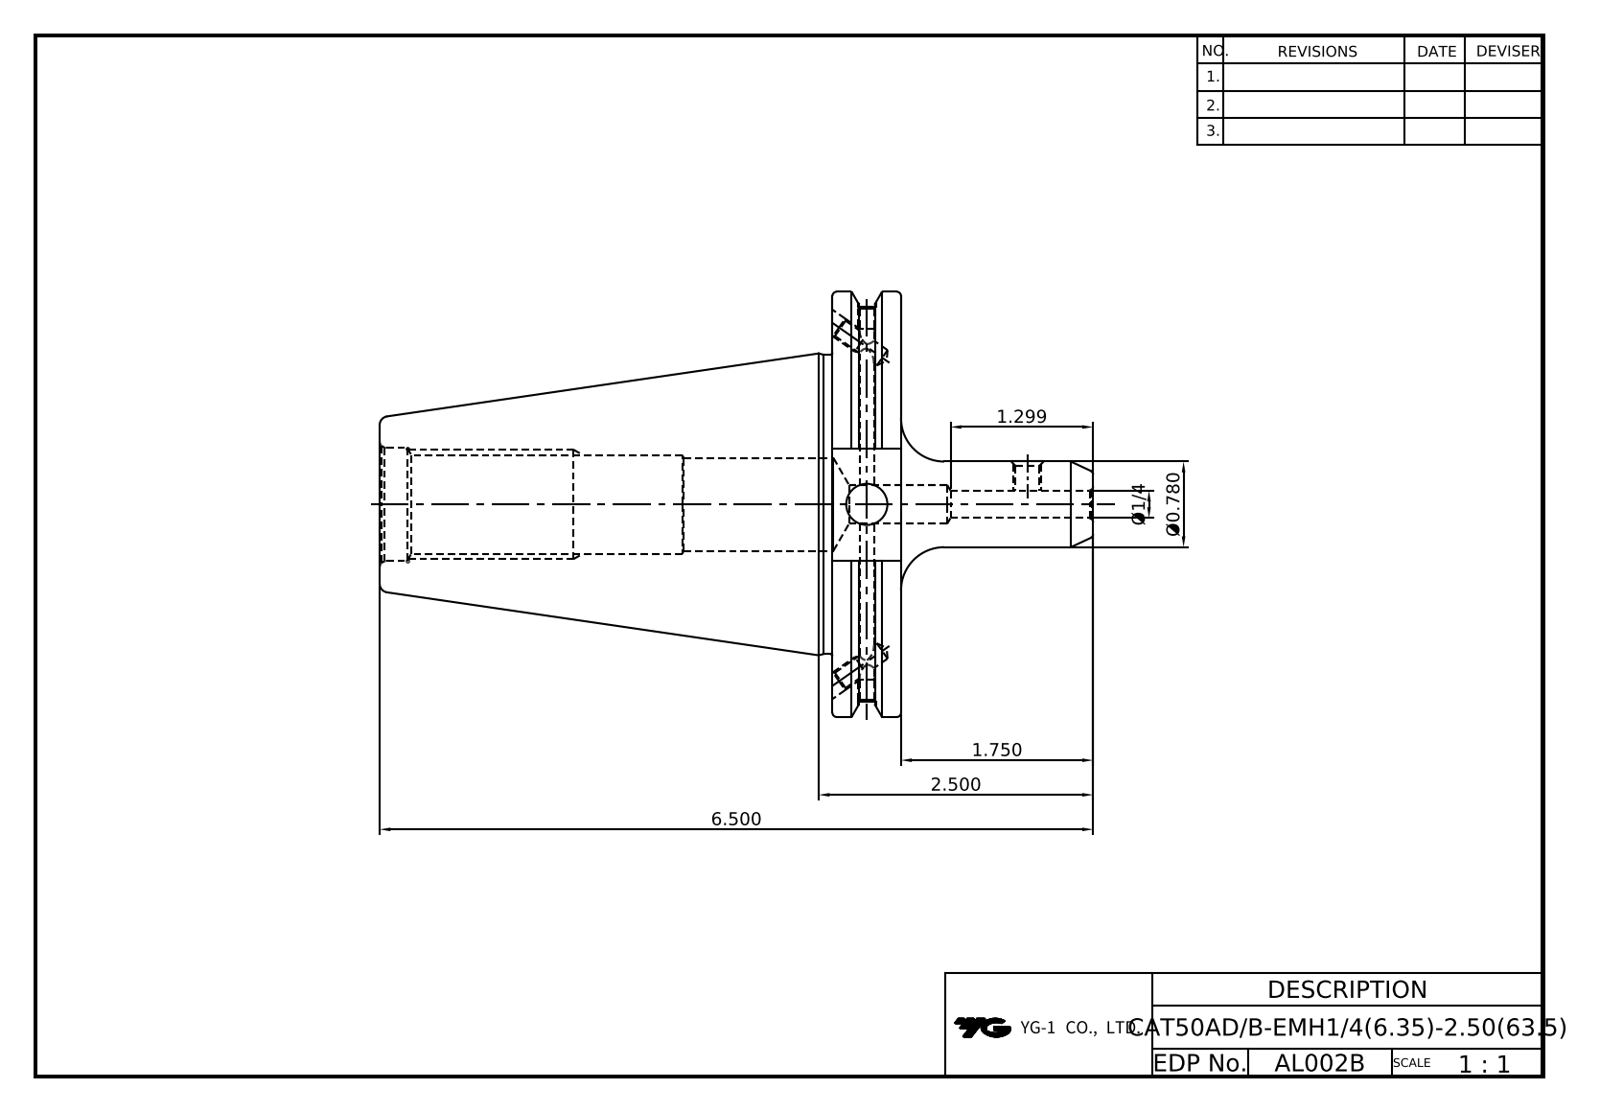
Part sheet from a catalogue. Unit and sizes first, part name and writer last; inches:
Units: inches
Overall size (bounding box): 6.5 × 3.875 × 3.728
Round holes (diameter × count): ⌀0.128 ×2, ⌀0.163 ×2, ⌀0.165 ×2, ⌀0.197 ×2, ⌀0.211 ×1, ⌀0.25 ×1, ⌀0.354 ×1, ⌀0.375 ×1, ⌀0.865 ×1, ⌀1.031 ×1
Round bosses / shafts (diameter × count): ⌀3.875 ×1, ⌀3.594 ×1, ⌀2.726 ×1, ⌀0.78 ×1
Main face-to-face distances: 0.625, 4.125, 4.75, 2.875, 1.02, 4.363, 0.238, 0.387, 4.514, 0.389
Volume: 20.46 in³ · Surface area: 74.75 in²
Bodies: 1 solid, 85 faces (35 planar, 26 cylindrical, 24 other)
Part name (STEP PRODUCT): LO-CAT50ADB-EMH6.35-63.5
STEP written by: Autodesk Inventor 2025 (AUTOMOTIVE_DESIGN)
